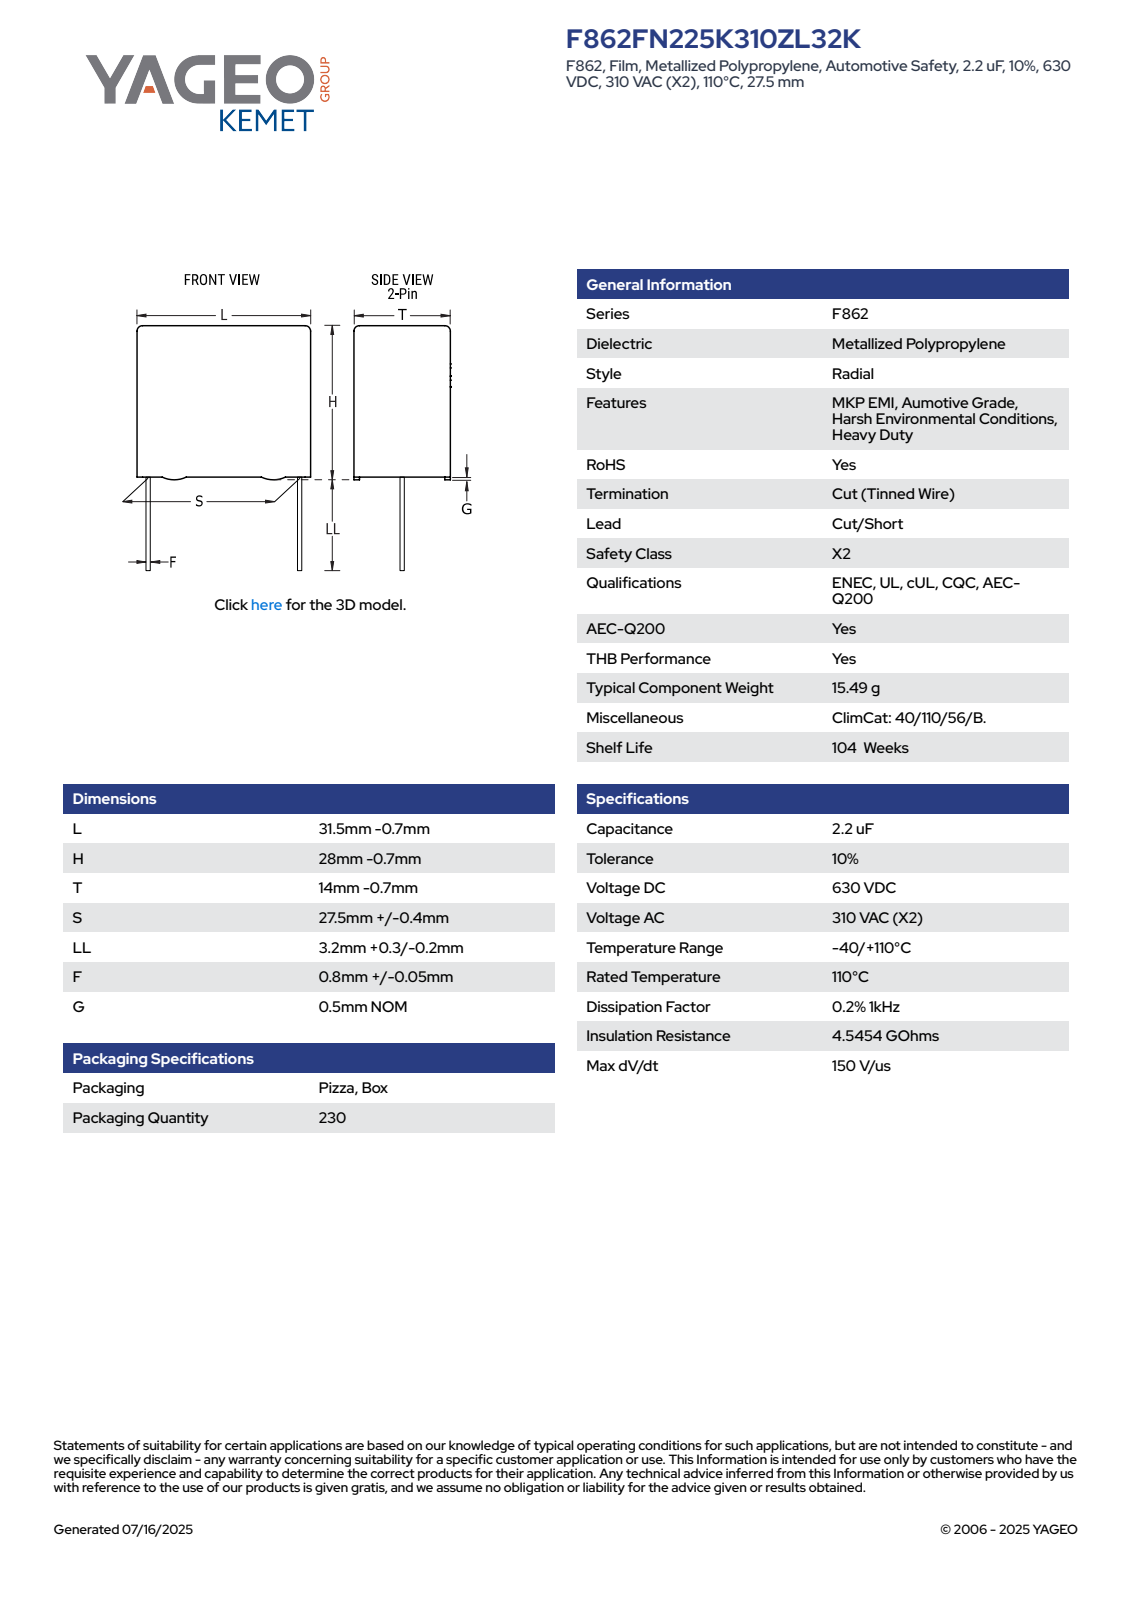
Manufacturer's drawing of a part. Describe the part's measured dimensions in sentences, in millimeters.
The part is named "CFR_RBG_31.5X28X14_L30.8H27.3T13.3S27.5LL3.5F0.85G0.5". Its 3-D file was written by "SolidWorks 2014 (AUTOMOTIVE_DESIGN)". It is 4 solids with 89 faces: 81 planar, 8 cylindrical and 0 other. Overall it measures 30.8 by 30.8 by 13.3 millimeters. Its volume is 10 986 cubic millimeters and its surface area 3 309 square millimeters. Round bosses or shafts: 2 of diameter 0.85. Partial cylindrical surfaces (rounded edges, fillets, slot ends): 4 of radius 0.5. The main face-to-face distances are 13.3, 26.8, 30.8, 13.31, 0.5, 27.3, 0.76, 12.54, 0.77, 11.78.
